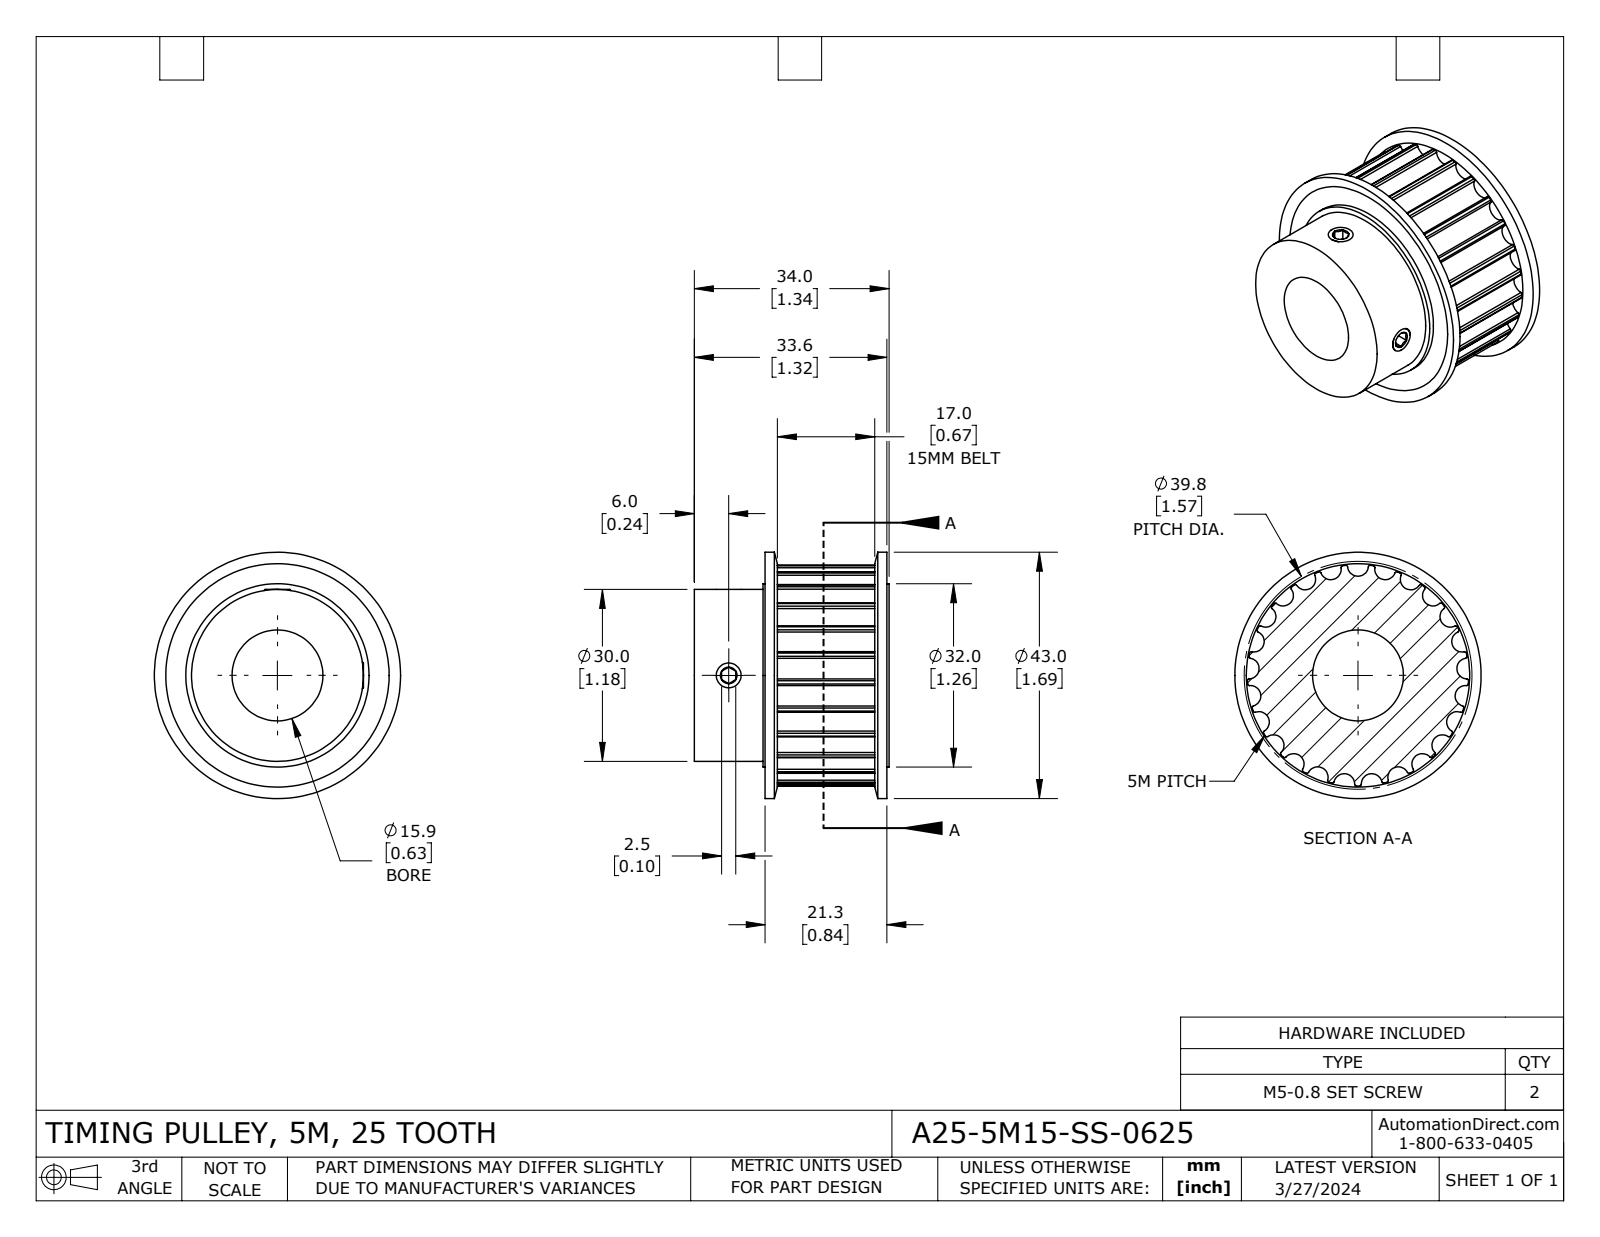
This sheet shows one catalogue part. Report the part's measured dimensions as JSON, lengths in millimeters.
{"part_name": "A25-5M15-SS-0625", "step_written_by": "SolidWorks 2021 (CONFIG_CONTROL_DESIGN)", "units": "millimeters", "bodies": {"solids": 5, "faces": 208, "planar": 25, "cylindrical": 149, "other": 34}, "overall_size": [43, 43, 34], "volume_mm3": 25224, "surface_area_mm2": 11631, "round_holes": [[4.2, 2], [15.88, 1], [32, 1]], "round_bosses_or_shafts": [[5, 2], [43, 1], [30, 1]], "partial_cylinders_radius": [[0.3, 50], [1.82, 25], [19.32, 1]], "face_to_face_distances": [1.6, 18.6, 2.5, 19.5, 17, 34, 31.5, 14.5, 0.9, 21.1]}
